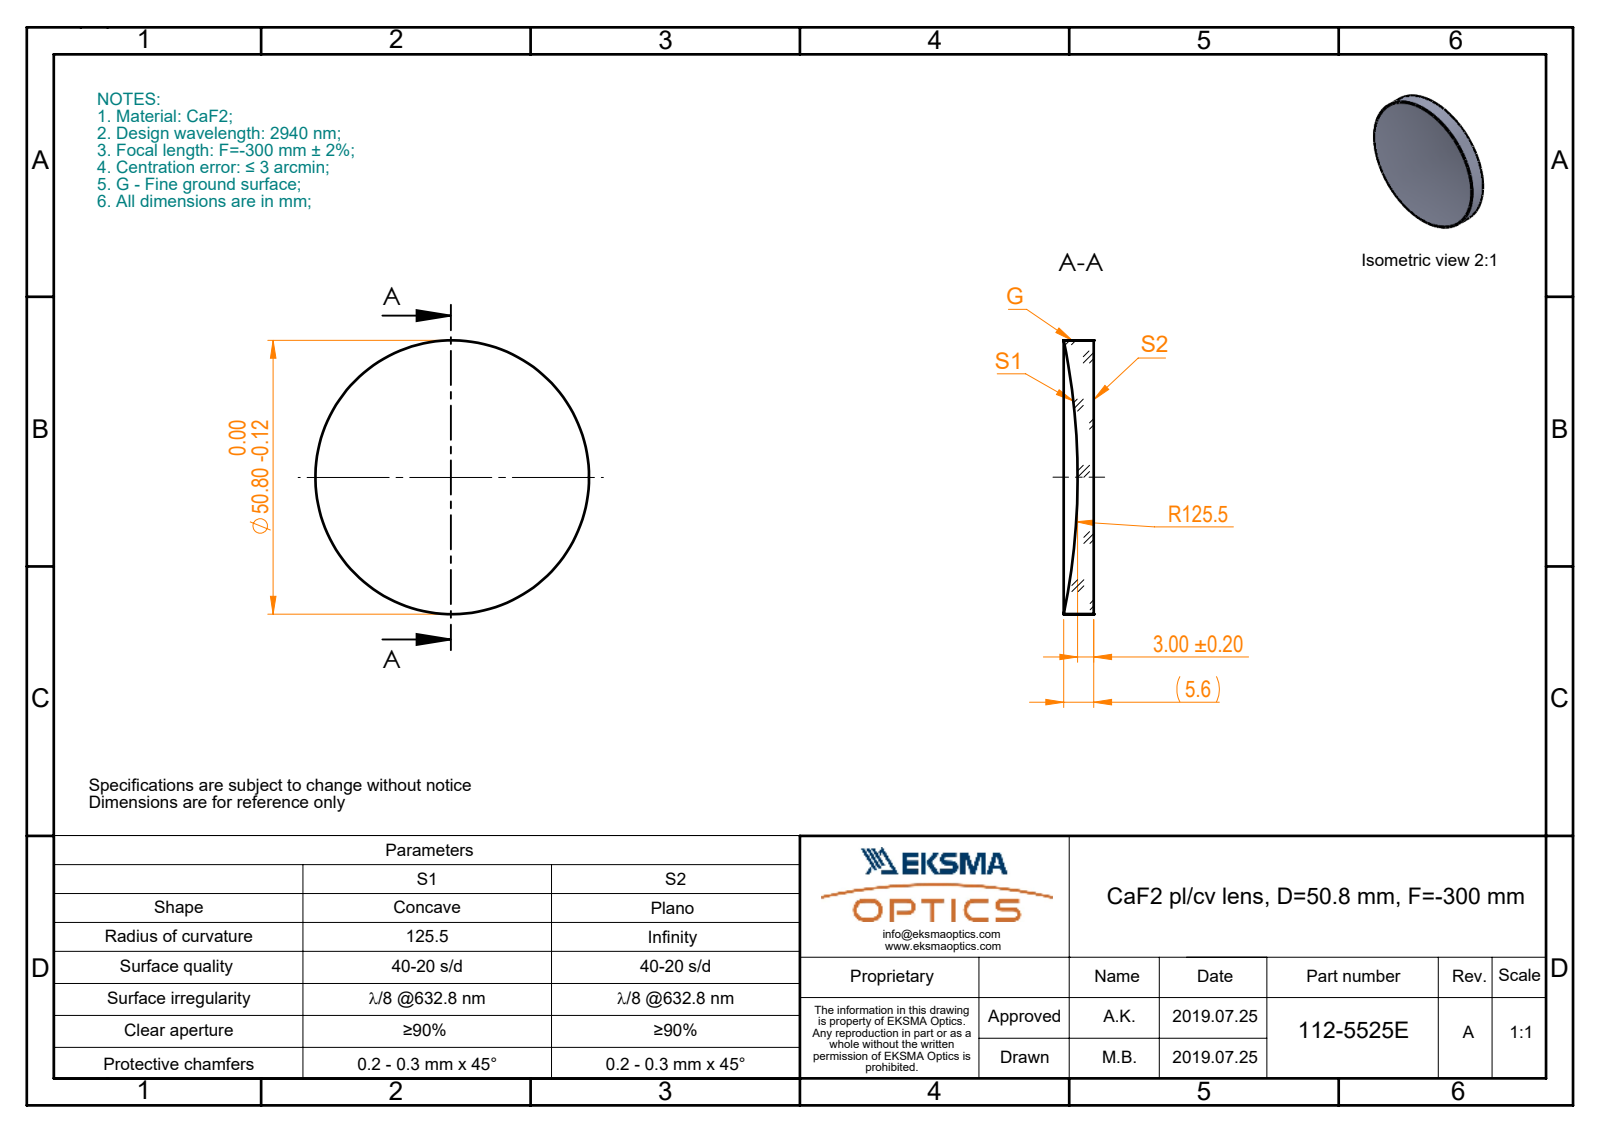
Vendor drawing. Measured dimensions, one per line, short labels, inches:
name: 112-5525E CaF2 pl-cv 50.8 F-300
written by: SolidWorks 2017 (CONFIG_CONTROL_DESIGN)
unit: in
bodies: 1 solid, 5 faces (1 planar, 2 cylindrical, 2 other)
size: 2 × 2 × 0.22
volume: 0.531 in³; area: 7.7 in²
bosses: 1× ⌀2
